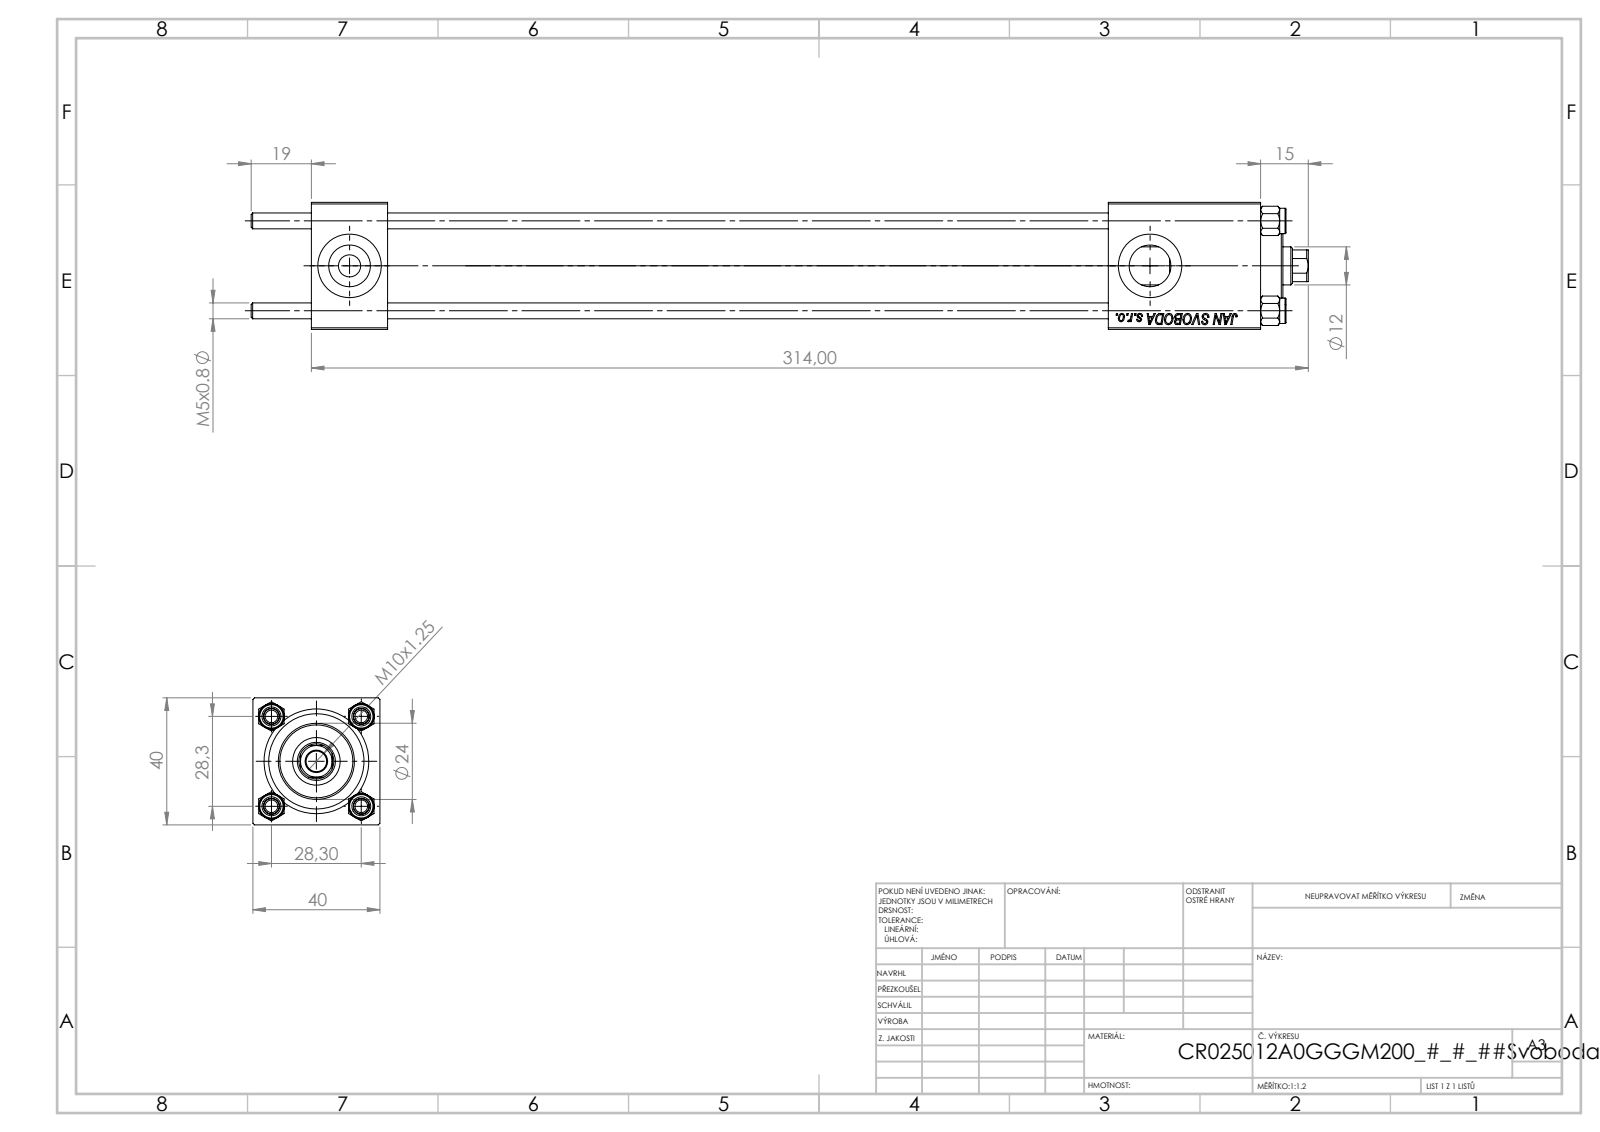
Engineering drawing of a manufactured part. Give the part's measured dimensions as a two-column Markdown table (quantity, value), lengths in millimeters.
| quantity | value |
| --- | --- |
| part name | NUT_M5; V215CR_BODY_A; V215CR_VCP; CR025_012_A_0_G_A_G_M_020_+#_##_TYCINKA (+1 more) |
| STEP written by | SolidWorks 2019 (CONFIG_CONTROL_DESIGN) |
| units | millimeters |
| bodies | 11 solids, 1132 faces (517 planar, 79 cylindrical, 536 other) |
| overall size | 333 × 40 × 40 |
| volume | 226 743 mm³ |
| surface area | 108 626 mm² |
| round holes (diameter × count) | 5 × 4, 20 × 3, 7 × 2, 13.16 × 2, 6.5 × 1, 12 × 1, 15 × 1, 25 × 1, 30 × 1 |
| round bosses / shafts (diameter × count) | 8 × 4, 31 × 1, 24 × 1 |
| partial cylindrical surfaces (radius × count) | 5.5 × 1 |
| main face-to-face distances | 40, 24, 299, 275, 270.3, 246.3, 28.7, 251, 227, 19.3 |
| hole center spacings | 20.01, 28.3, 40.02, 252.16 |
